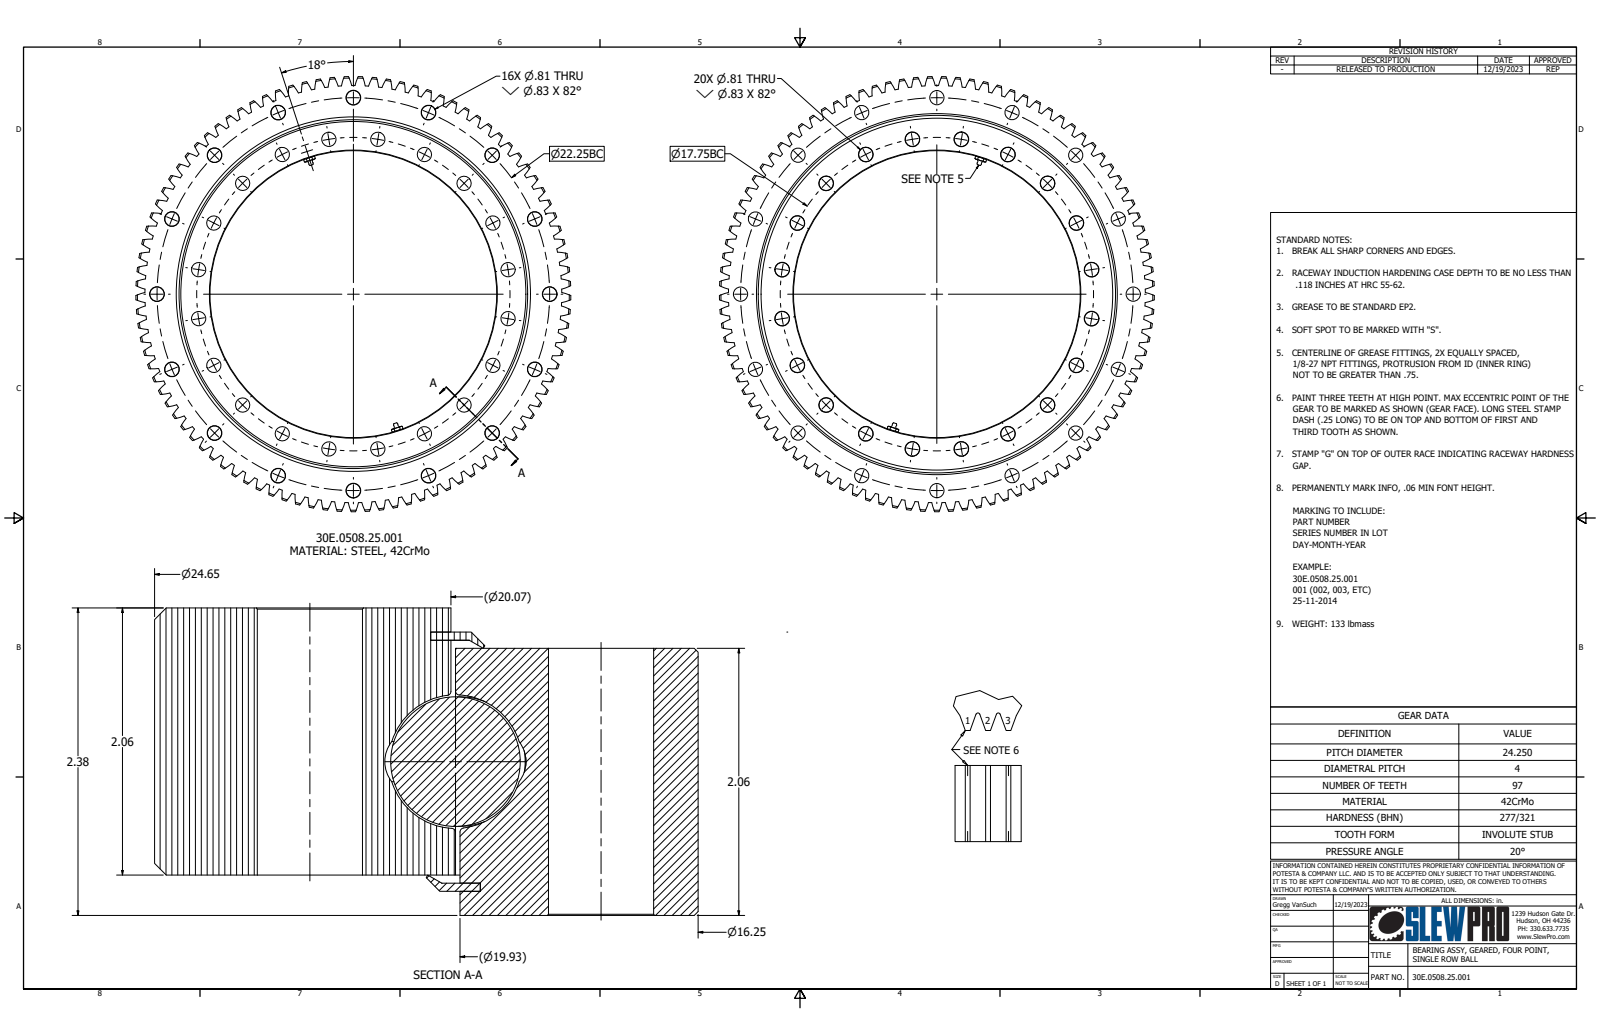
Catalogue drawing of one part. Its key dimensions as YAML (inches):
part_name: "30E.0508.25.001; Spur Gears1; HGF_11"
step_written_by: "Autodesk Inventor 2026 (AUTOMOTIVE_DESIGN)"
units: inches
bodies: {solids: 7, faces: 909, planar: 36, cylindrical: 444, other: 429}
overall_size: [24.649, 24.647, 2.375]
volume: 468.8
surface_area: 1746
round_holes:
  - {diameter: 0.813, count: 36}
  - {diameter: 0.063, count: 2}
  - {diameter: 0.109, count: 2}
  - {diameter: 1.126, count: 1}
  - {diameter: 16.25, count: 1}
  - {diameter: 19.617, count: 1}
  - {diameter: 20, count: 1}
  - {diameter: 20.07, count: 1}
  - {diameter: 20.383, count: 1}
round_bosses_or_shafts:
  - {diameter: 20.383, count: 1}
  - {diameter: 19.93, count: 1}
  - {diameter: 19.617, count: 1}
  - {diameter: 1.125, count: 1}
partial_cylinders:
  - {radius: 3.495, count: 194}
  - {radius: 11.812, count: 1}
  - {radius: 12.325, count: 1}
face_to_face_distances: [2.063, 0.312, 1.751, 2.375, 1.939, 0.063, 0.187, 2.188, 0.125, 1.876]
hole_center_spacings: [4.341, 12.361, 18.5, 2.777, 8.515, 8.515, 8.875, 11.125]
